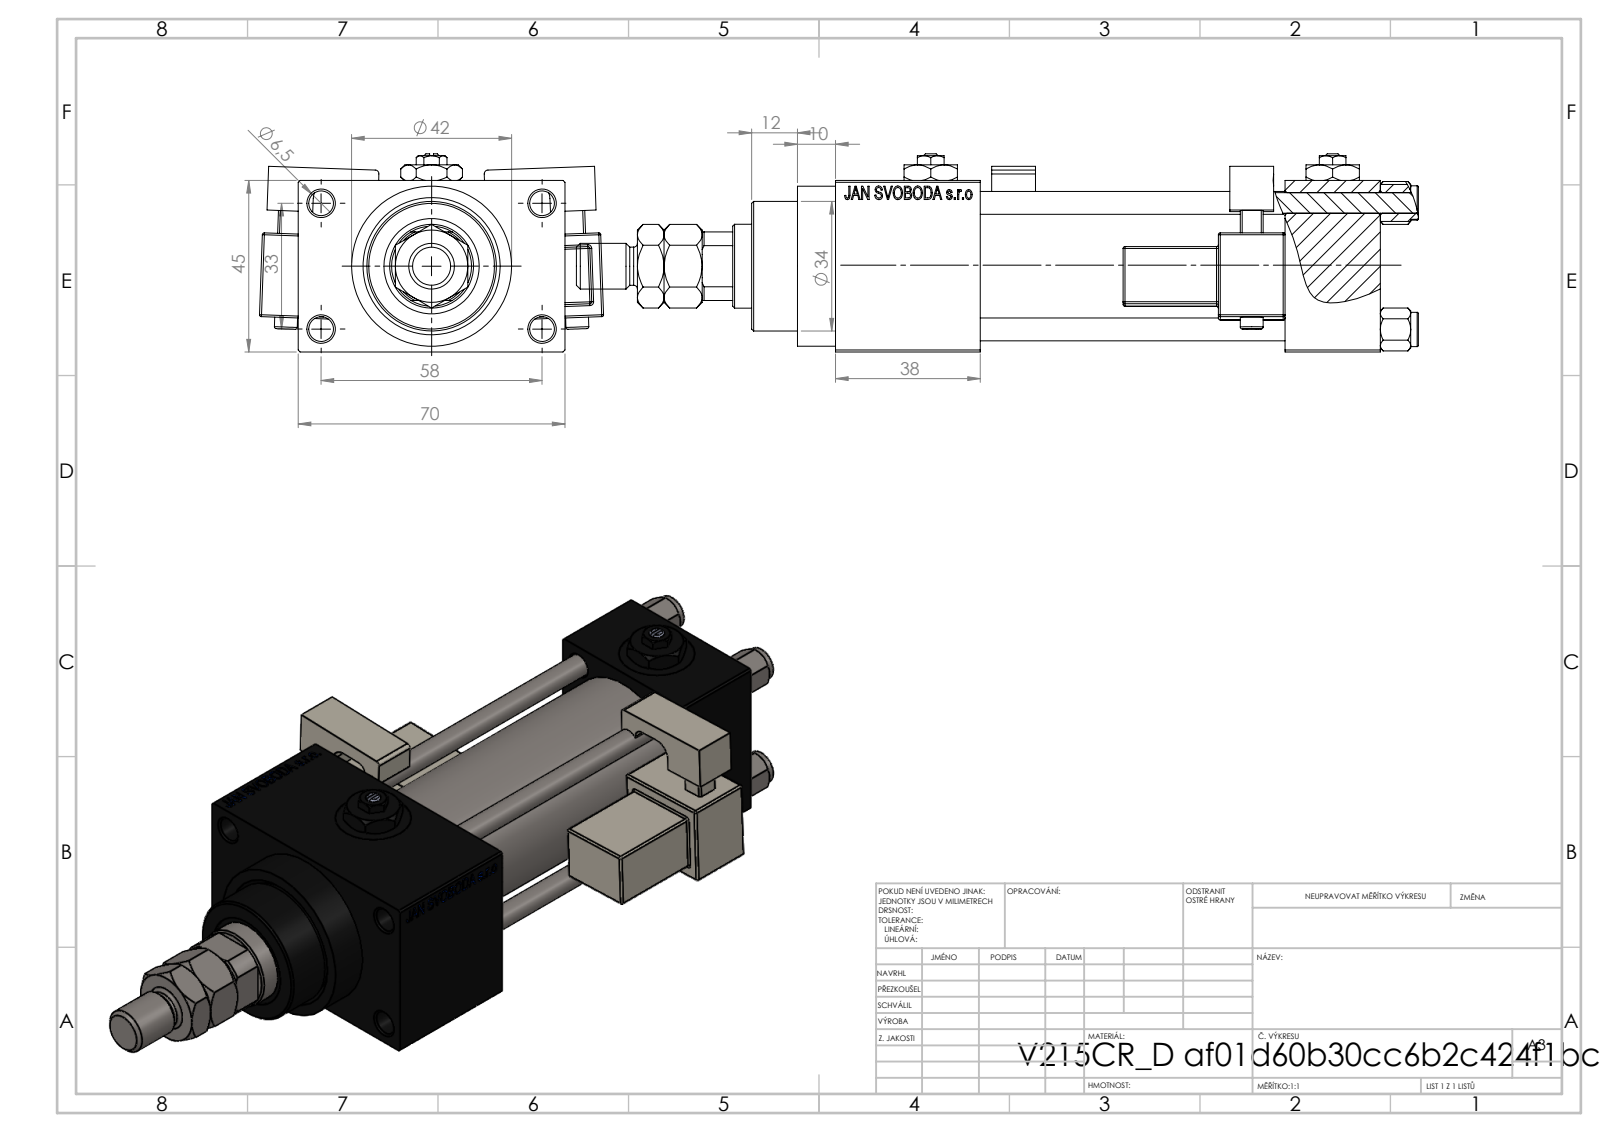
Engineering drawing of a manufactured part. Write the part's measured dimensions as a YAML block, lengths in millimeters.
part_name: "V215CR_D_Body; V215_VC_A; V215CR_VCP_D; V215CR_MSU (+4 more)"
step_written_by: "SolidWorks 2019 (CONFIG_CONTROL_DESIGN)"
units: millimeters
bodies: {solids: 16, faces: 1410, planar: 619, cylindrical: 163, other: 628}
overall_size: [221, 90.31, 52]
volume: 313950
surface_area: 106875
round_holes:
  - {diameter: 6, count: 4}
  - {diameter: 6.5, count: 4}
  - {diameter: 13.16, count: 4}
  - {diameter: 20, count: 4}
  - {diameter: 7, count: 3}
  - {diameter: 10.5, count: 1}
  - {diameter: 22, count: 1}
  - {diameter: 24, count: 1}
  - {diameter: 25, count: 1}
  - {diameter: 32, count: 1}
  - {diameter: 33, count: 1}
round_bosses_or_shafts:
  - {diameter: 9, count: 4}
  - {diameter: 6, count: 2}
  - {diameter: 42, count: 1}
  - {diameter: 38, count: 1}
  - {diameter: 34, count: 1}
  - {diameter: 12, count: 1}
  - {diameter: 10, count: 1}
partial_cylinders:
  - {radius: 0.5, count: 48}
  - {radius: 1, count: 2}
  - {radius: 2.5, count: 2}
  - {radius: 4, count: 2}
  - {radius: 10.5, count: 1}
face_to_face_distances: [45, 25, 80, 12.5, 3, 105, 57.5, 38, 118, 143]
hole_center_spacings: [12.4, 23.48, 33.2, 33.37, 35.35, 45.6, 56.35, 33]
